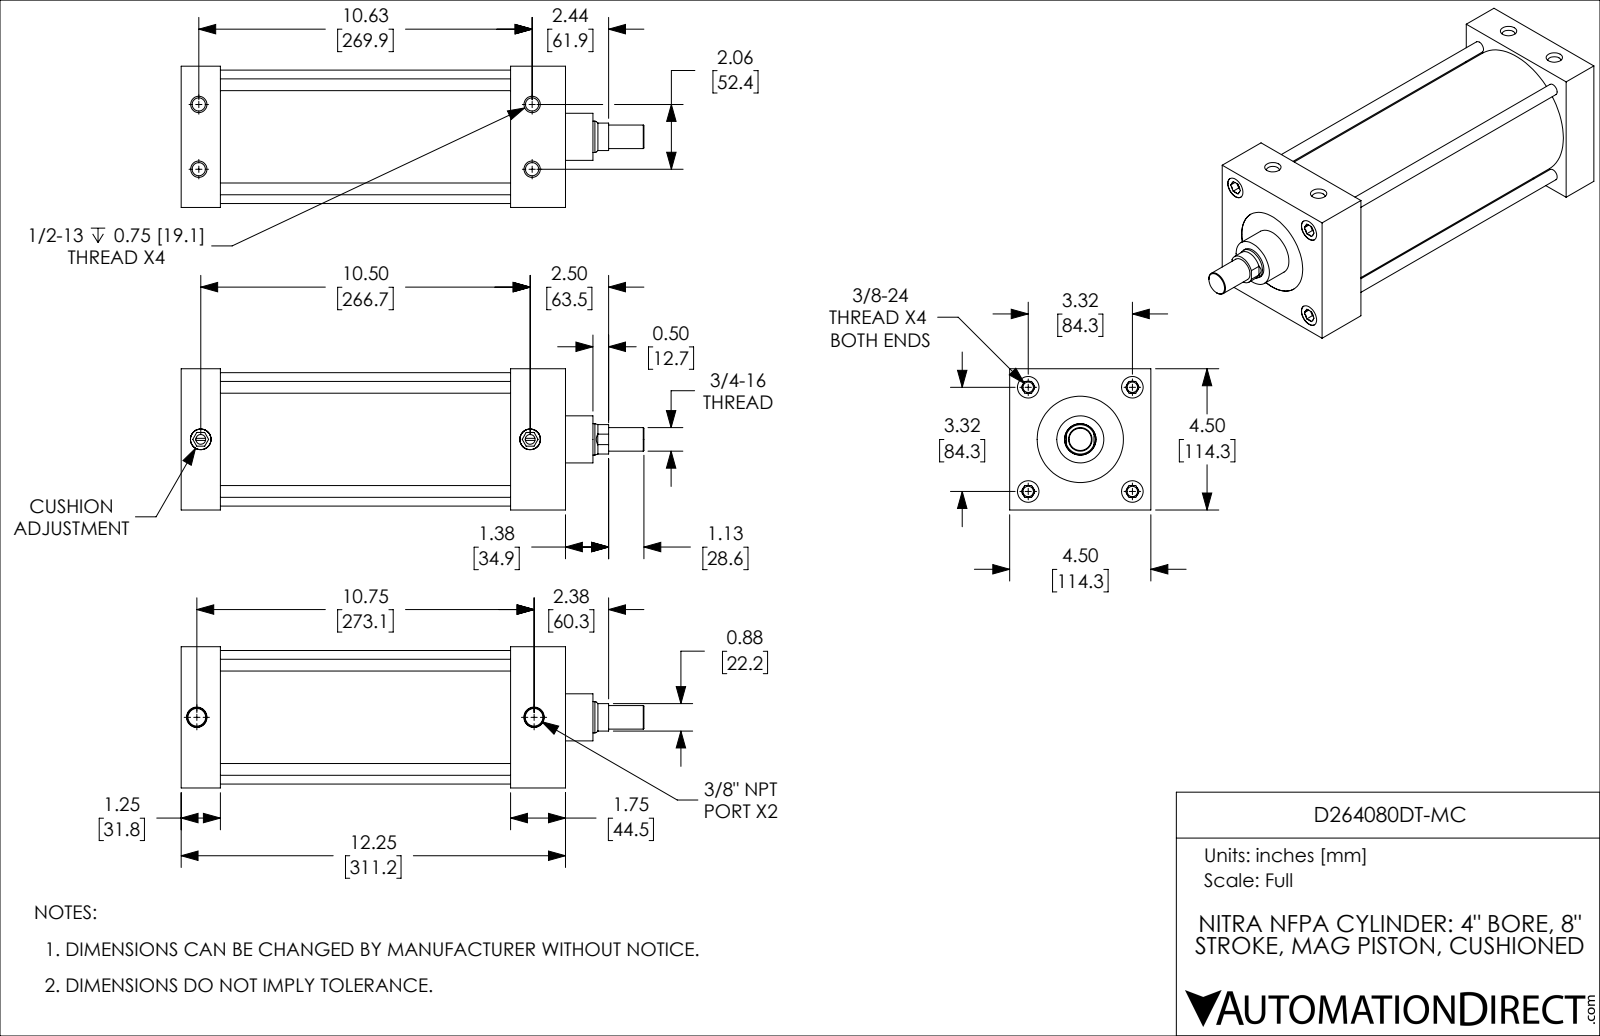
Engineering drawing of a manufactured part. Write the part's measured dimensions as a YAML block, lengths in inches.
part_name: "D264080DT-MC; D264080DT-MC_BODY; D264080DT-MC_CUSHION; D264080DT-MC_PISTON_KK1"
step_written_by: "SolidWorks 2019 (CONFIG_CONTROL_DESIGN)"
units: inches
bodies: {solids: 4, faces: 246, planar: 90, cylindrical: 78, other: 78}
overall_size: [14.75, 4.5, 4.5]
volume: 101.7
surface_area: 526.9
round_holes:
  - {diameter: 0.332, count: 4}
  - {diameter: 0.422, count: 4}
  - {diameter: 0.687, count: 4}
  - {diameter: 0.312, count: 2}
  - {diameter: 0.562, count: 2}
  - {diameter: 0.656, count: 2}
  - {diameter: 1.001, count: 1}
  - {diameter: 2.75, count: 1}
  - {diameter: 4.001, count: 1}
round_bosses_or_shafts:
  - {diameter: 0.375, count: 4}
  - {diameter: 0.657, count: 2}
  - {diameter: 4.251, count: 1}
  - {diameter: 3.999, count: 1}
  - {diameter: 1.5, count: 1}
  - {diameter: 0.999, count: 1}
  - {diameter: 0.75, count: 1}
partial_cylinders:
  - {radius: 0.469, count: 1}
face_to_face_distances: [1.25, 4.5, 10.5, 9.25, 12.25, 11, 1.75, 2.5, 8, 9.75]
hole_center_spacings: [1.033, 2.347, 3.32, 10.737, 2.062, 4.695, 10.625, 10.823]
